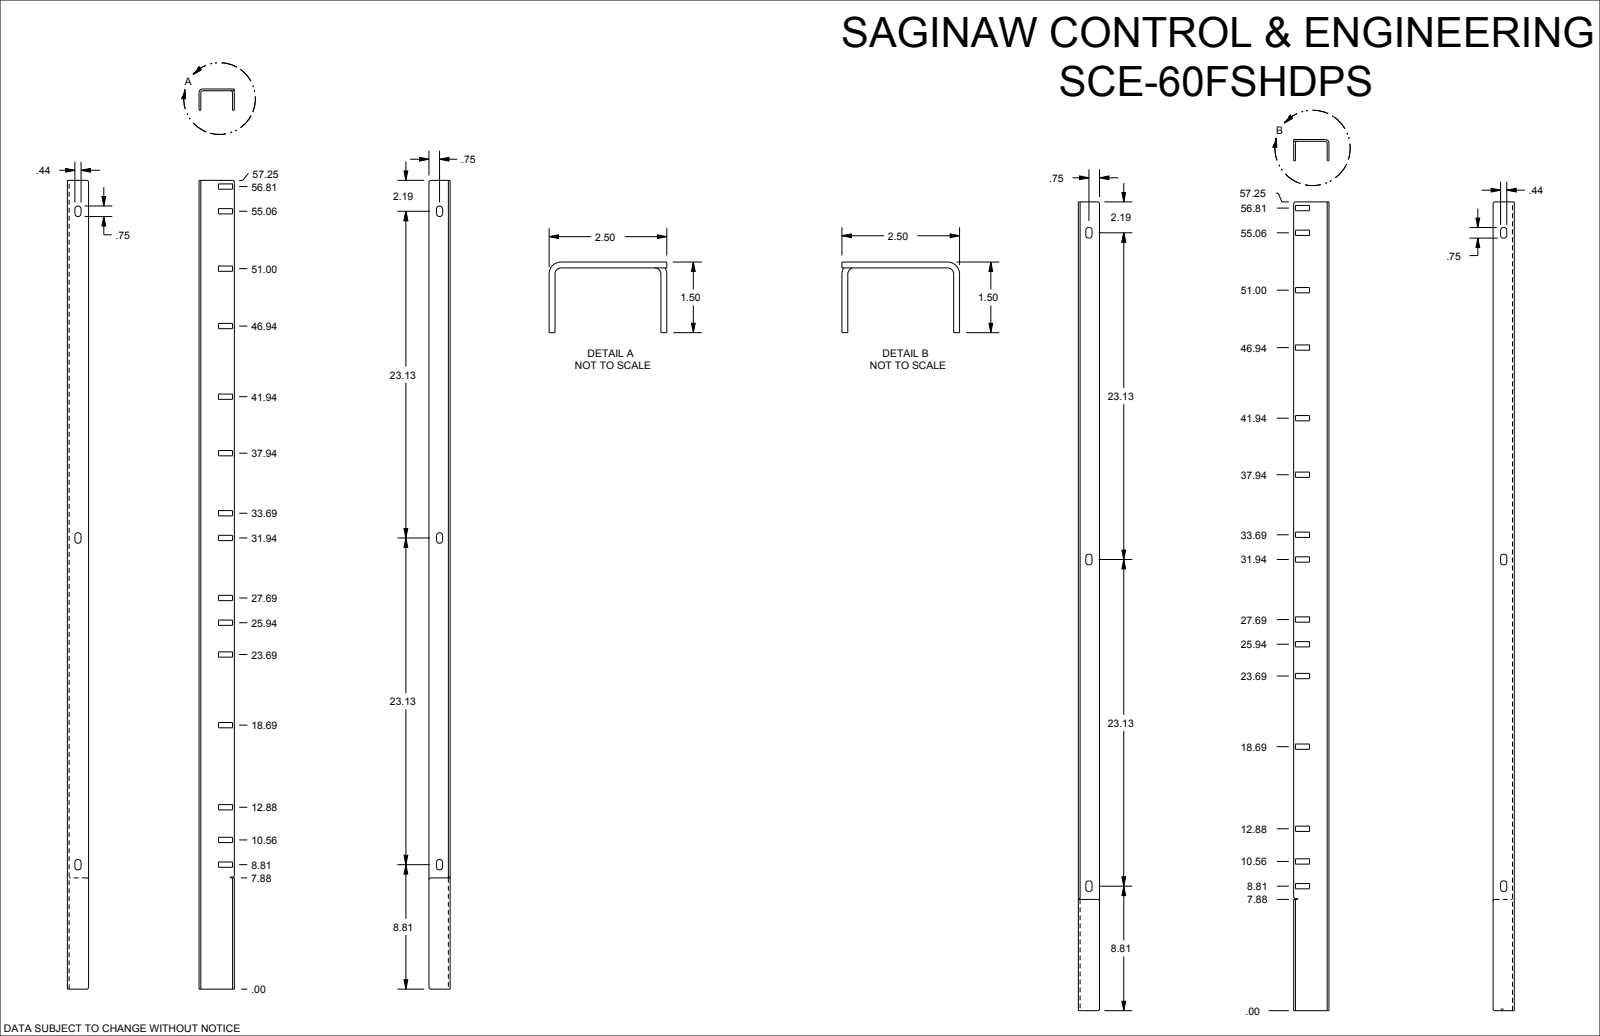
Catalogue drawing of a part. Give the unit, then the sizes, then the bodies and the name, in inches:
Units: inches
Overall size (bounding box): 57.25 × 12 × 1.5
Partial cylindrical surfaces — rounded edges, fillets, slot ends (radius × count): R0.015 ×120, R0.188 ×12, R0.13 ×8, R0.125 ×6, R0.219 ×6, R0.03 ×3, R0.031 ×3, R0.255 ×3
Main face-to-face distances: 0.125, 0.125, 11.875, 12, 11.75, 9.375, 2.5, 9.5, 2.375, 2.375
Volume: 55.2 in³ · Surface area: 926.2 in²
Bodies: 2 solids, 332 faces (168 planar, 164 cylindrical, 0 other)
Part name (STEP PRODUCT): SCE-60FSHDPS
STEP written by: SolidWorks 2019 (CONFIG_CONTROL_DESIGN)
